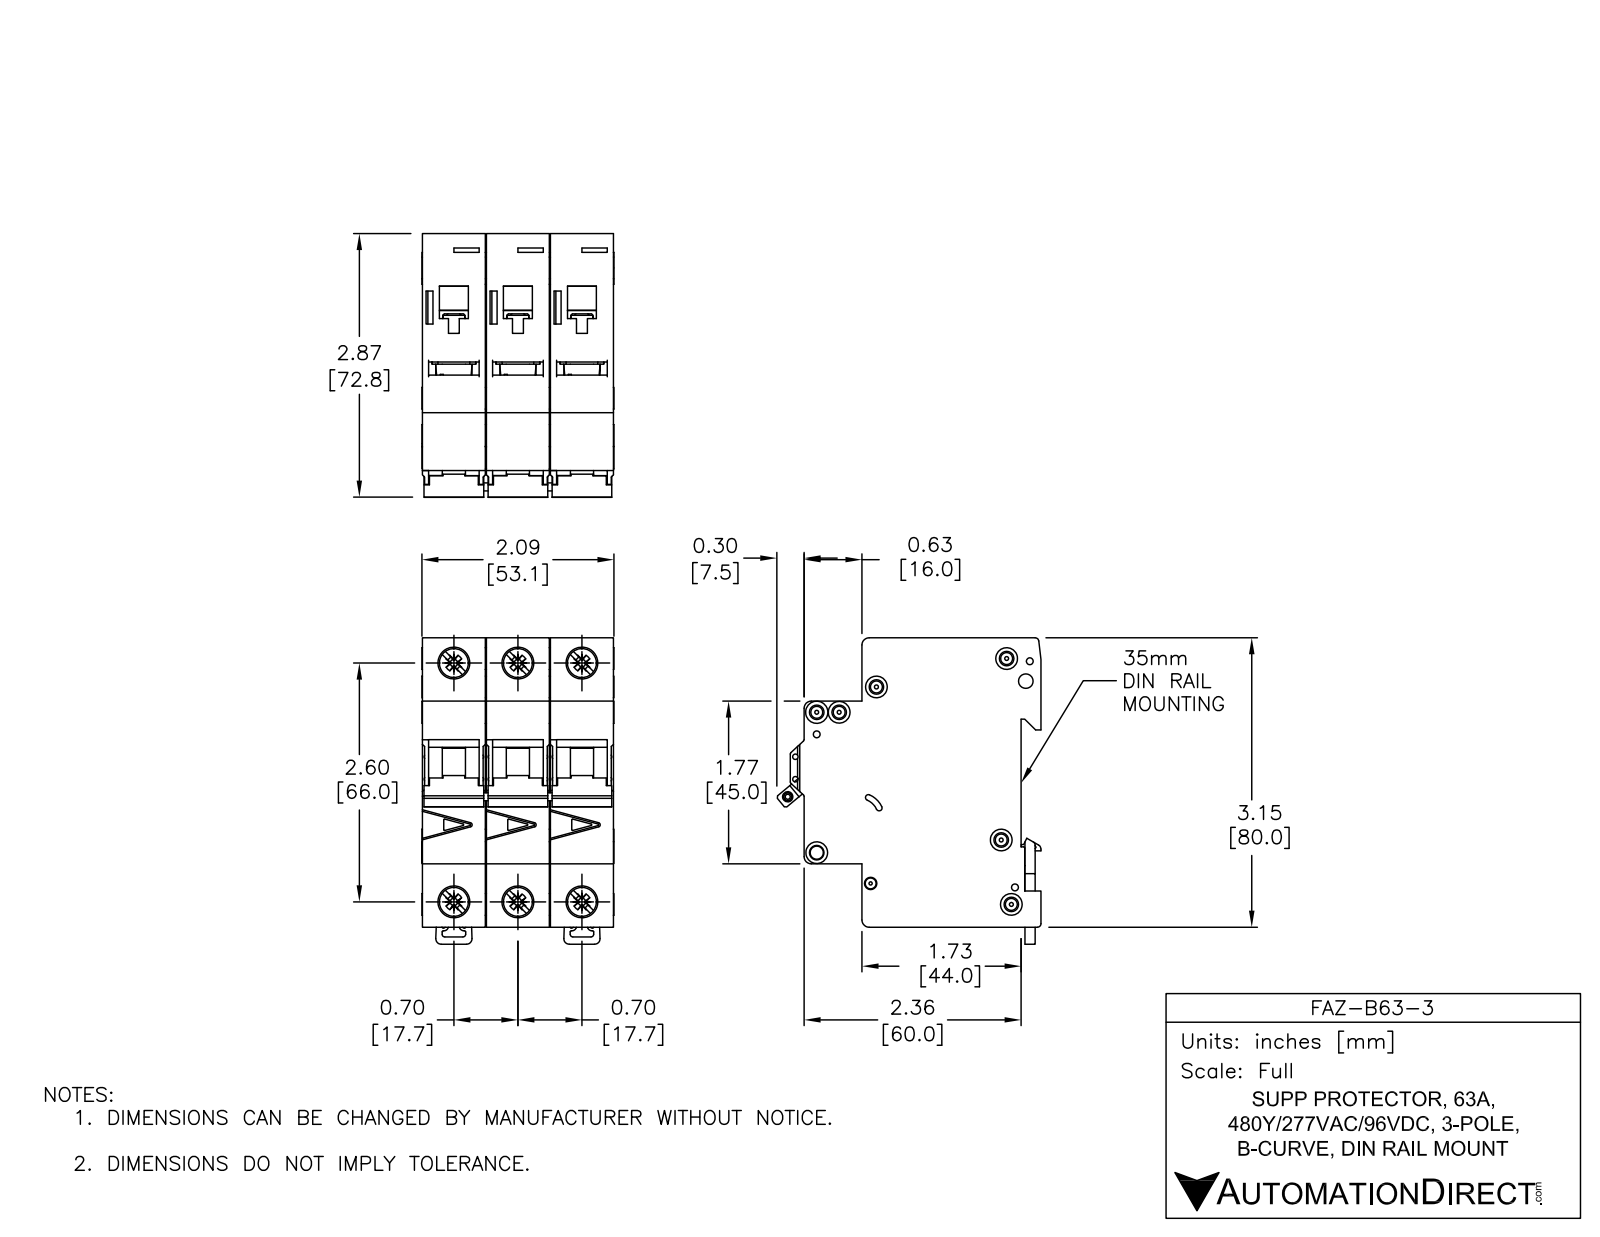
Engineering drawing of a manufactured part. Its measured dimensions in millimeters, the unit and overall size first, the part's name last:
Units: millimetres
Overall size (bounding box): 84.78 × 73.04 × 53.1
Round holes (diameter × count): ⌀3.6 ×6, ⌀8.2 ×4, ⌀1.9 ×3, ⌀1.09 ×2, ⌀1.5 ×2, ⌀4 ×2, ⌀7.15 ×2, ⌀2.15 ×1, ⌀2.2 ×1, ⌀2.55 ×1, ⌀3.3 ×1, ⌀3.4 ×1
Round bosses / shafts (diameter × count): ⌀6 ×4, ⌀2.5 ×3, ⌀8.2 ×2
Partial cylindrical surfaces — rounded edges, fillets, slot ends (radius × count): R0.25 ×68, R0.5 ×25, R1 ×12, R2 ×12, R0.2 ×11, R1.8 ×3, R0.8 ×2, R3 ×2
Main face-to-face distances: 17.7, 17.5, 35.4, 35.2, 52.9, 17.9, 79.48, 5.5, 49.5, 44
Hole centre spacings: 17.7, 68.33, 66, 6.2, 13.64, 35.4, 74.89, 4.81
Volume: 224 680 mm³ · Surface area: 58 052 mm²
Bodies: 11 solids, 1650 faces (697 planar, 590 cylindrical, 363 other)
Part name (STEP PRODUCT): FAZ-B63-3
STEP written by: SolidWorks 2014 (AUTOMOTIVE_DESIGN)
